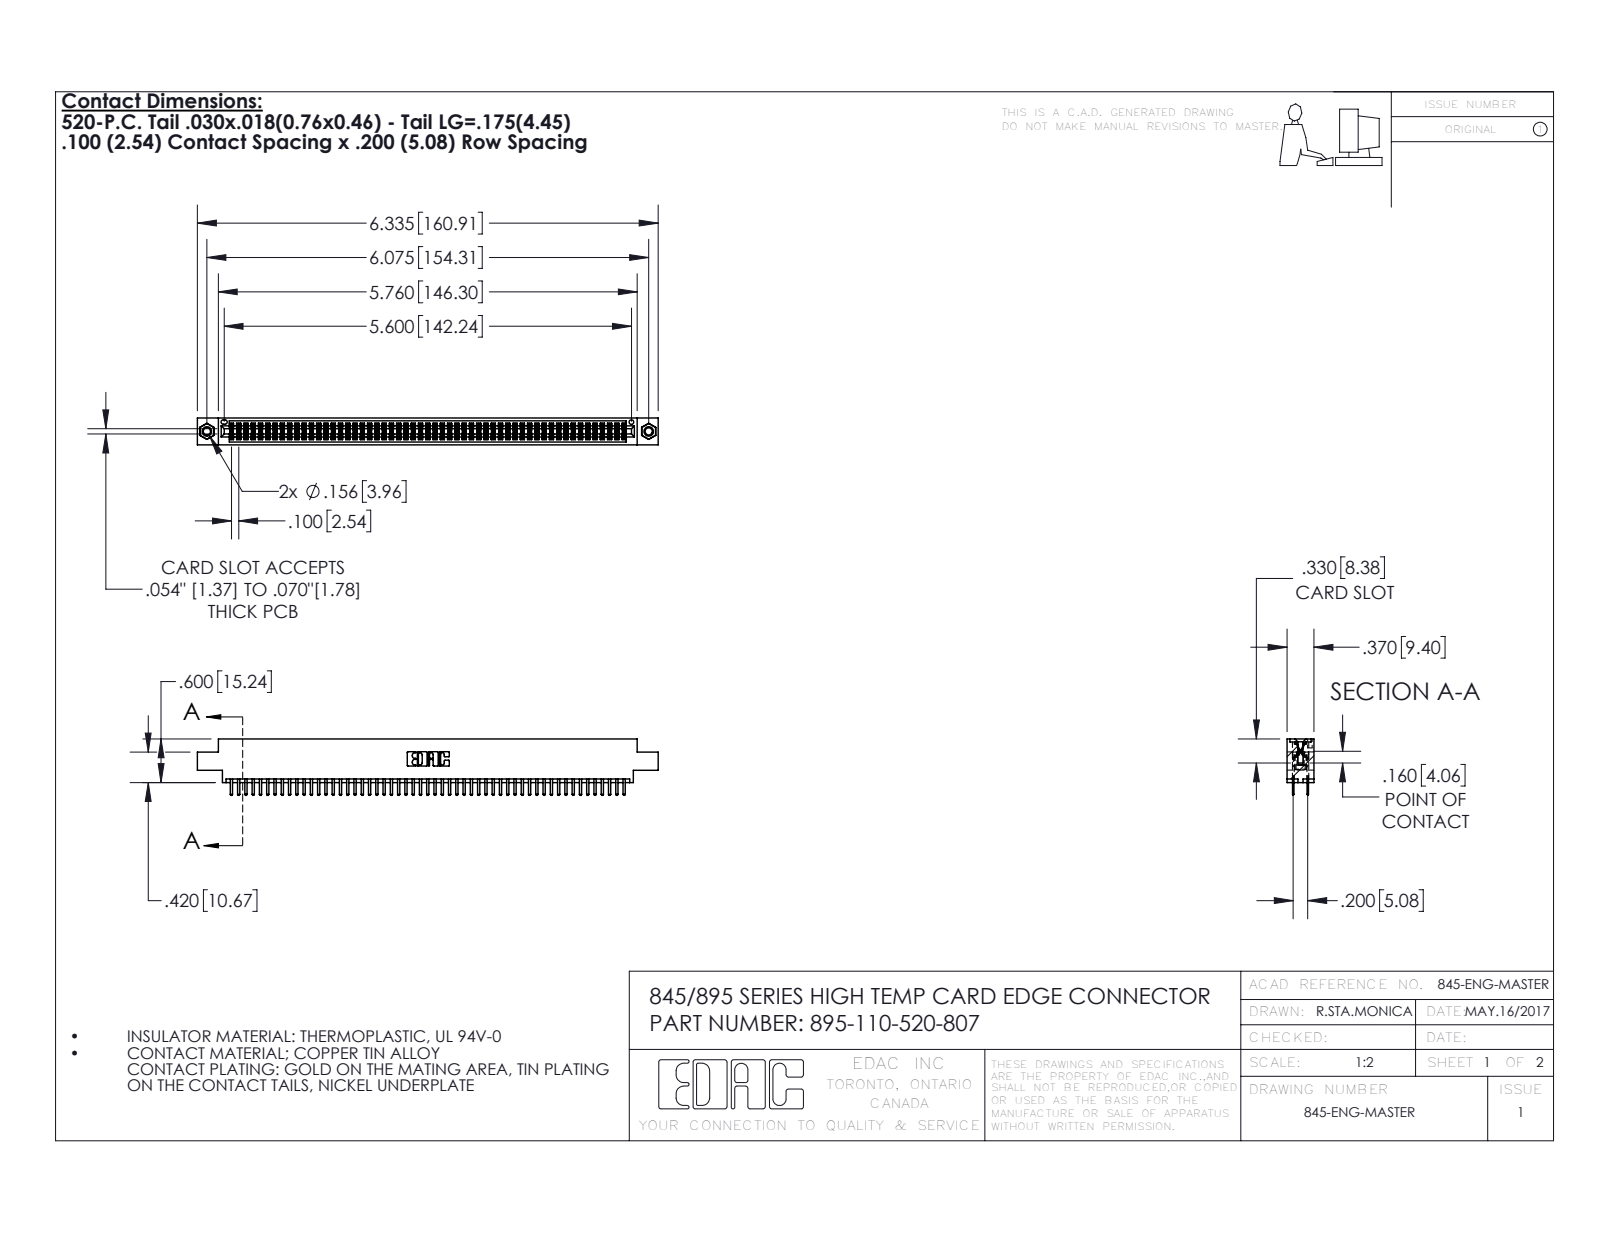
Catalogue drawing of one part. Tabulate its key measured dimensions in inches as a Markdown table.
| quantity | value |
| --- | --- |
| part name | 345-292-001_345-293-120; 395-110-520-807; 345-250-001_345-250-005-103; 345 Part_0.170 Offset - 0.156 Dia-TI |
| STEP written by | SolidWorks 2016 (CONFIG_CONTROL_DESIGN) |
| units | inches |
| bodies | 113 solids, 6130 faces (3966 planar, 2148 cylindrical, 16 other) |
| overall size | 6.335 × 0.775 × 0.37 |
| volume | 0.951 in³ |
| surface area | 36.18 in² |
| round holes (diameter × count) | 0.098 × 2, 0.125 × 2, 0.156 × 2, 0.064 × 1 |
| round bosses / shafts (diameter × count) | 0.155 × 2 |
| partial cylindrical surfaces (radius × count) | 0.006 × 165, 0.01 × 114, 0.01 × 22, 0.007 × 6, 0.031 × 6, 0.026 × 3, 0.014 × 2, 0.019 × 2 |
| main face-to-face distances | 0.072, 0.298, 0.2, 0.37, 0.098, 0.272, 0.025, 0.225, 0.022, 0.072 |
| hole center spacings | 0.27, 5.839, 6.075 |
